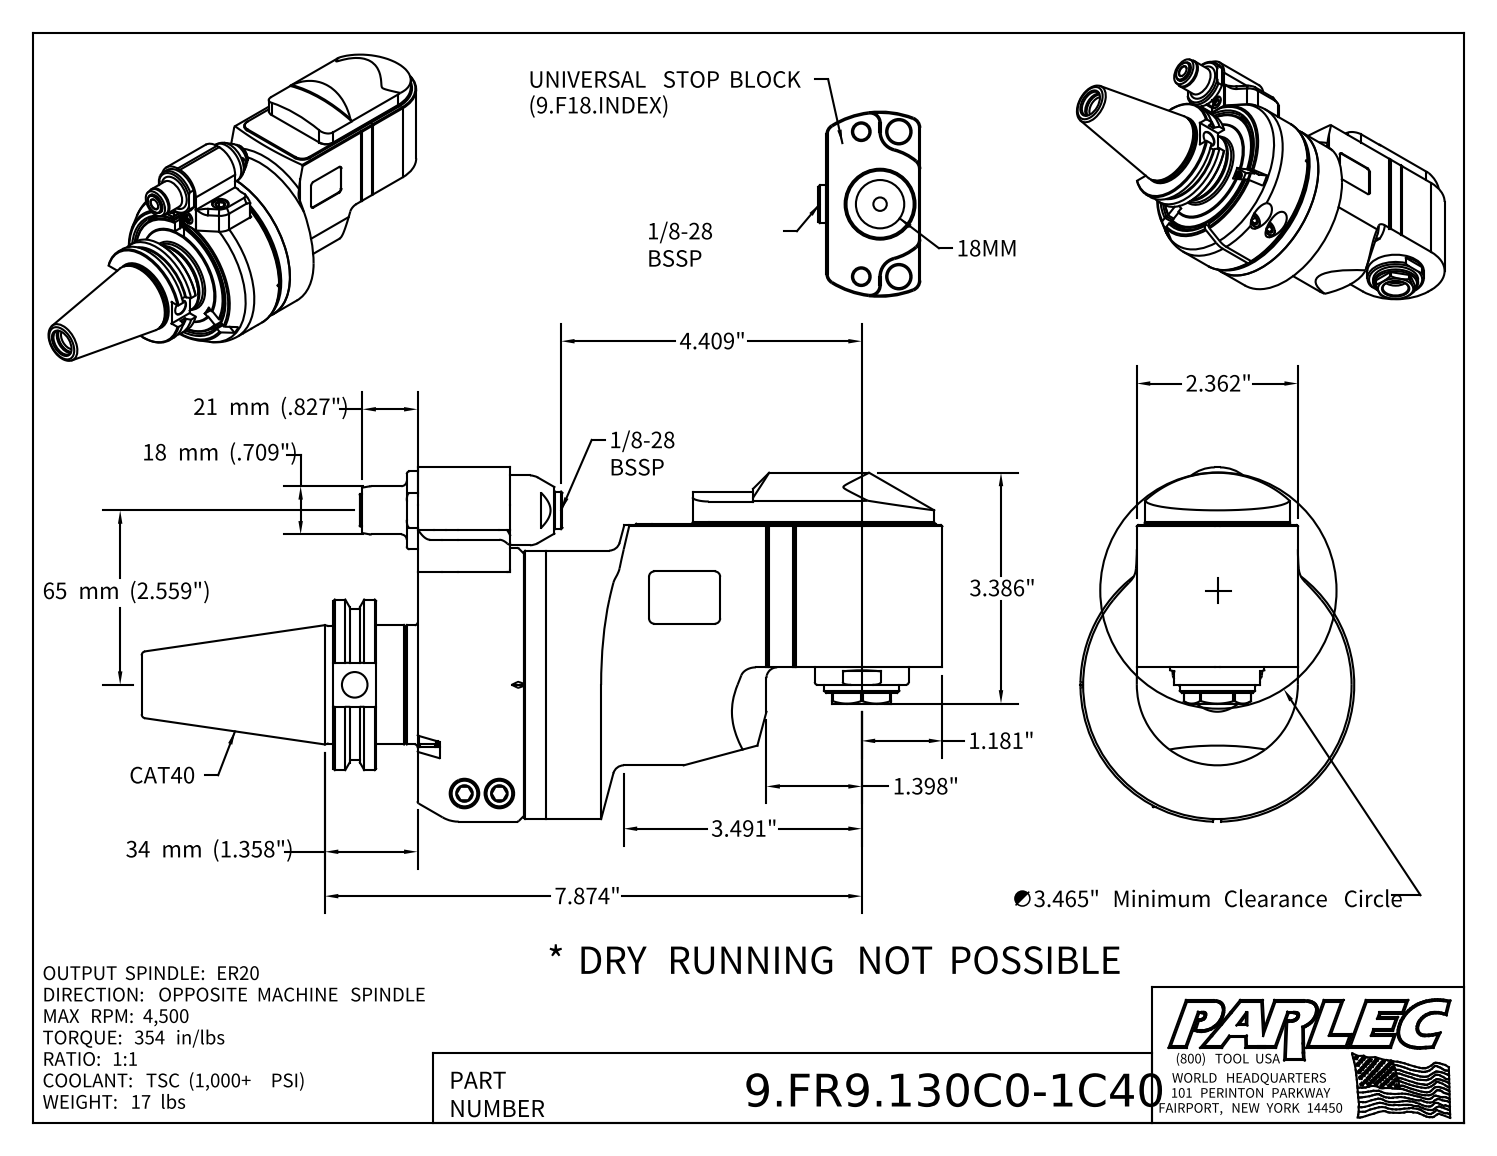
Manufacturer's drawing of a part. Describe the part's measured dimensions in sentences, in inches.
The part is named "9.FR9.130C0-1C40; FR9-13C". Its 3-D file was written by "Autodesk Inventor 2022 (AUTOMOTIVE_DESIGN)". It is 26 solids with 720 faces: 302 planar, 200 cylindrical and 218 other. Overall it measures 11.742 by 5.196 by 4.016 inches. Its volume is 75.6 cubic inches and its surface area 279.5 square inches. Round holes: 7 of diameter 0.197, 6 of diameter 0.165, 4 of diameter 0.126, 4 of diameter 0.13, 3 of diameter 0.236, 3 of diameter 0.256, 3 of diameter 0.315, 3 of diameter 0.807, 2 of diameter 0.102, 2 of diameter 0.266, 2 of diameter 0.409, 2 of diameter 0.433. Round bosses or shafts: 5 of diameter 0.394, 4 of diameter 0.236, 4 of diameter 0.157, 2 of diameter 0.866, 2 of diameter 0.709, 2 of diameter 0.472, 2 of diameter 0.197, 1 of diameter 4.016. Partial cylindrical surfaces (rounded edges, fillets, slot ends): 14 of radius 0.039, 6 of radius 0.118, 5 of radius 0.157, 4 of radius 0.079, 2 of radius 0.02, 2 of radius 0.236, 2 of radius 0.315, 2 of radius 0.551. The main face-to-face distances are 1.22, 2.362, 0.335, 0.02, 0.276, 1.398, 0.118, 1.555, 0.039, 1.122. The hole center spacings are 0.325, 0.459, 0.276, 0.472, 0.504, 0.65, 0.74, 0.838.
